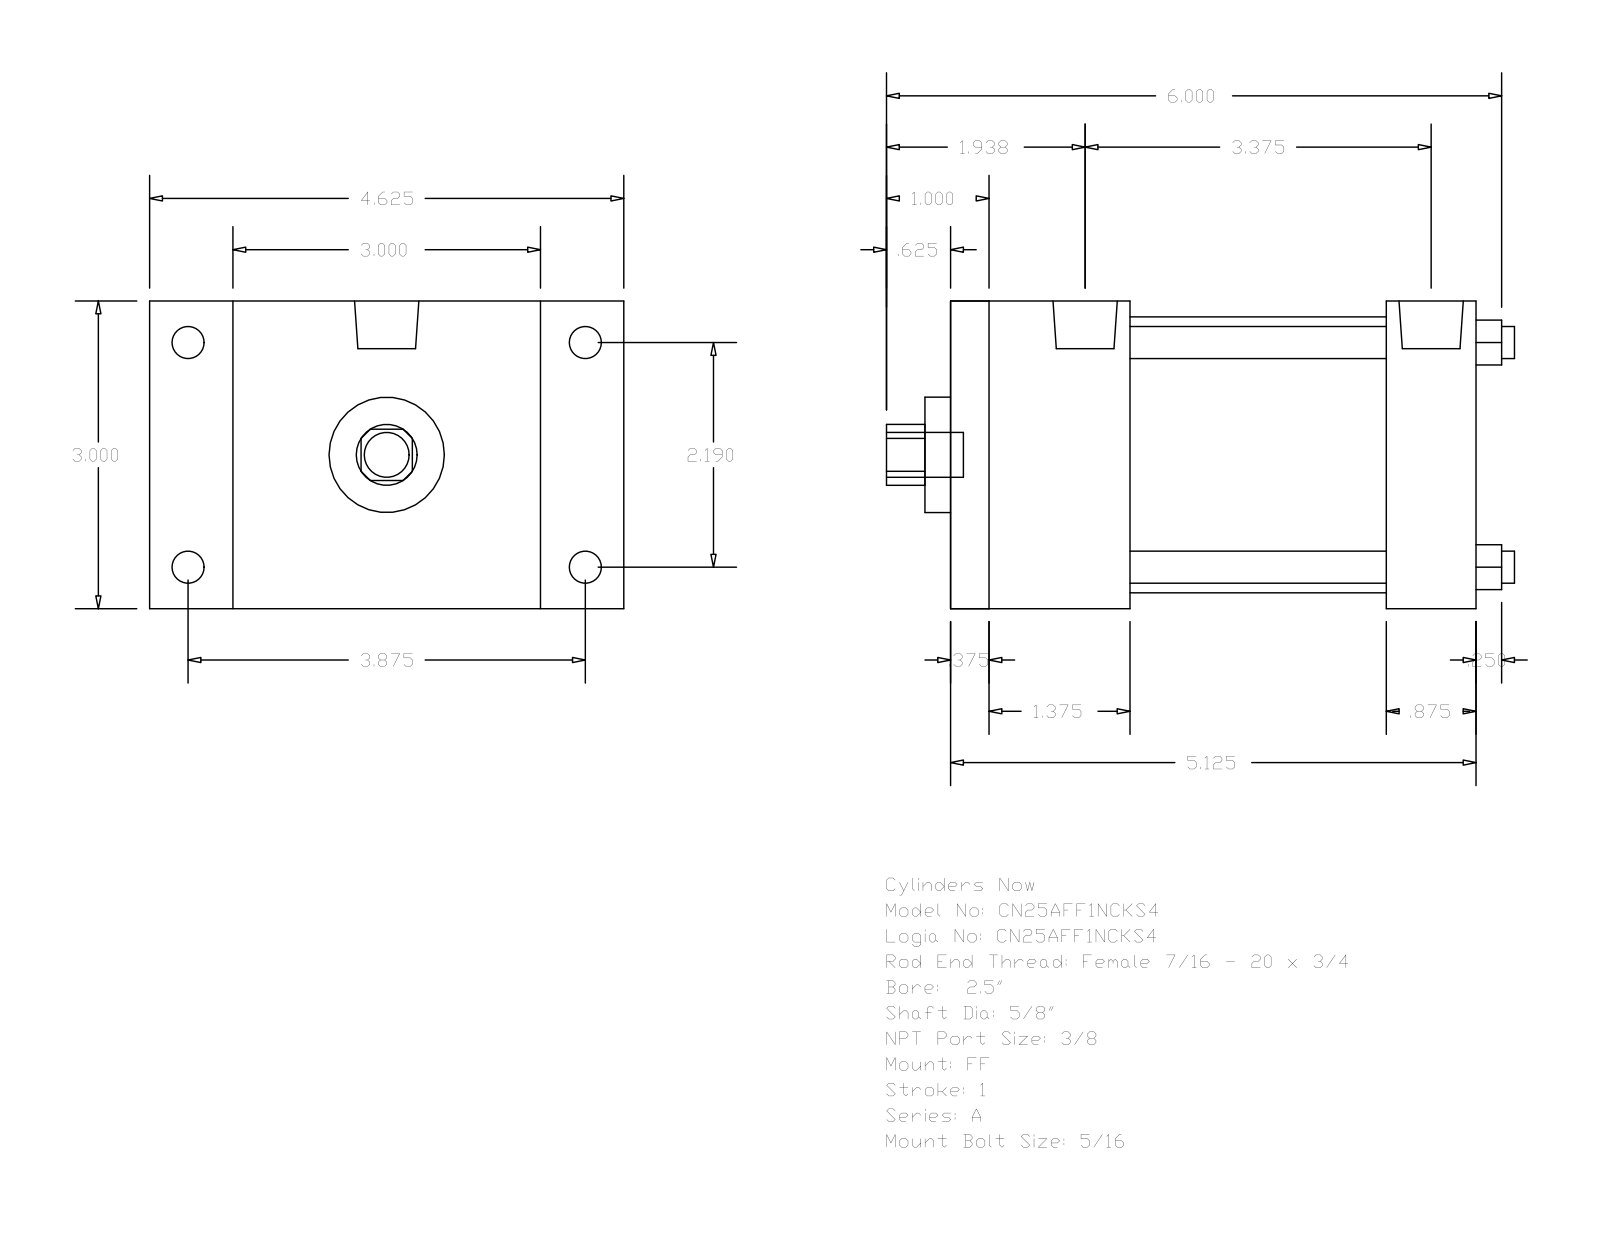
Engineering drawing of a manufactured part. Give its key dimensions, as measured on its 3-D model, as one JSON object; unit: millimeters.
{"part_name": "A_FF__0250_0.625", "step_written_by": "GSSL Pune (CONFIG_CONTROL_DESIGN)", "units": "millimeters", "bodies": {"solids": 0, "faces": 92, "planar": 64, "cylindrical": 28, "other": 0}, "overall_size": [155.57, 117.47, 76.2], "round_holes": [[7.94, 4], [15.88, 1], [28.57, 1], [68.33, 1]], "round_bosses_or_shafts": [[7.94, 4], [5.56, 4], [15.93, 2], [11.11, 1]], "partial_cylinders_radius": [[7.54, 1]], "face_to_face_distances": [76.2, 130.17, 9.52, 120.65, 44.45, 107.95, 34.93, 98.43, 63.5, 85.72], "hole_center_spacings": [39.33, 55.62, 78.66]}
